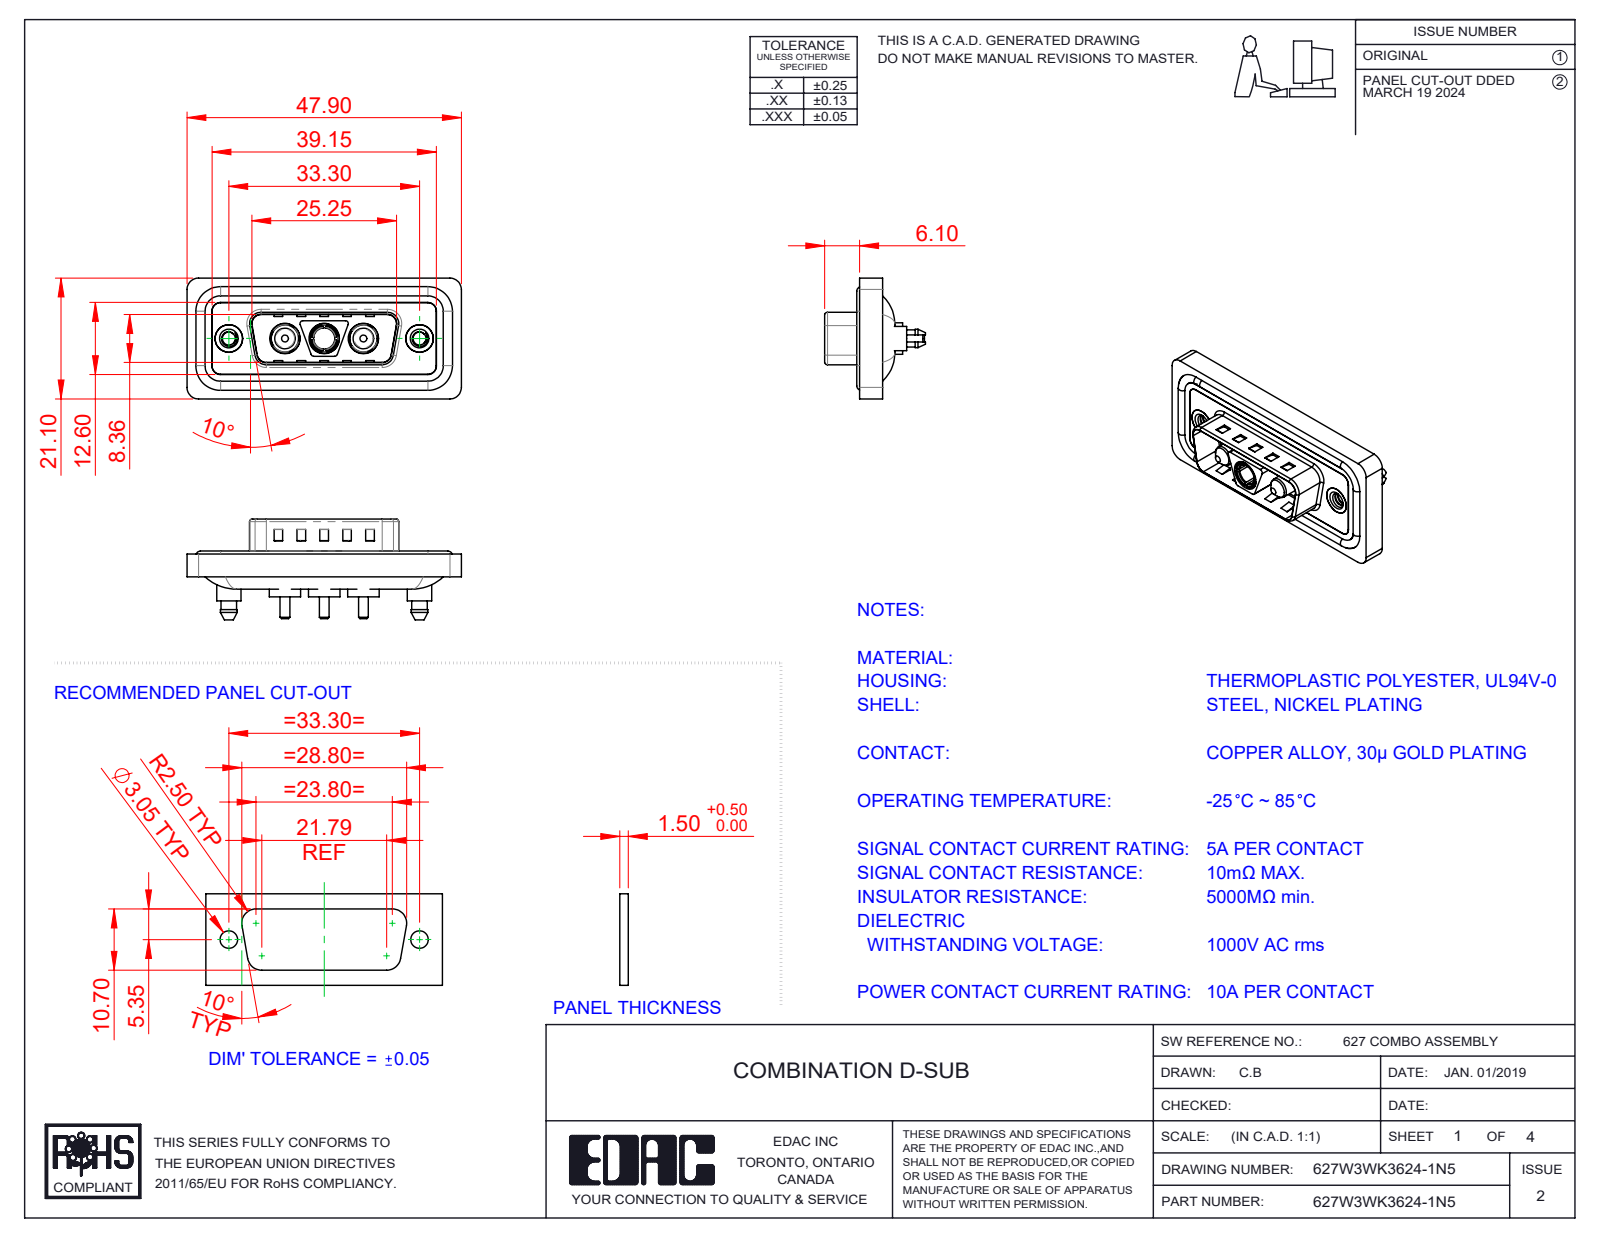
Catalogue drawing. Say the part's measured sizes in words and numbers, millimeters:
The part is named "627Combo Housing_3WK3; 627Combo Waterproof Housing_15 Contacts; Power Socket_10A S; 627Combo Shell Front_15 Contacts (+4 more)". Its 3-D file was written by "SolidWorks 2023 (CONFIG_CONTROL_DESIGN)". It is 13 solids with 659 faces: 247 planar, 282 cylindrical and 130 other. Overall it measures 47.9 by 21.1 by 17.6 millimeters. Its volume is 5 778 cubic millimeters and its surface area 9 422 square millimeters. Round holes: 3 of diameter 4.85, 3 of diameter 5.3, 2 of diameter 2.26, 2 of diameter 4, 2 of diameter 4.8, 2 of diameter 5, 1 of diameter 3.7. Round bosses or shafts: 4 of diameter 1.6, 3 of diameter 5.5, 3 of diameter 5.2, 3 of diameter 4.75, 3 of diameter 3.75, 3 of diameter 1.7, 2 of diameter 5.4, 2 of diameter 4.9. Partial cylindrical surfaces (rounded edges, fillets, slot ends): 28 of radius 1.5, 20 of radius 2, 12 of radius 0.5, 10 of radius 1.6, 4 of radius 0.25, 4 of radius 0.6, 4 of radius 0.65, 4 of radius 0.9. The main face-to-face distances are 0.4, 1.5, 1.1, 0.5, 1.6, 3.1, 2.9, 4, 0.7, 0.82. The hole center spacings are 6.85, 9.8, 16.65, 23.5, 13.7, 33.3.
